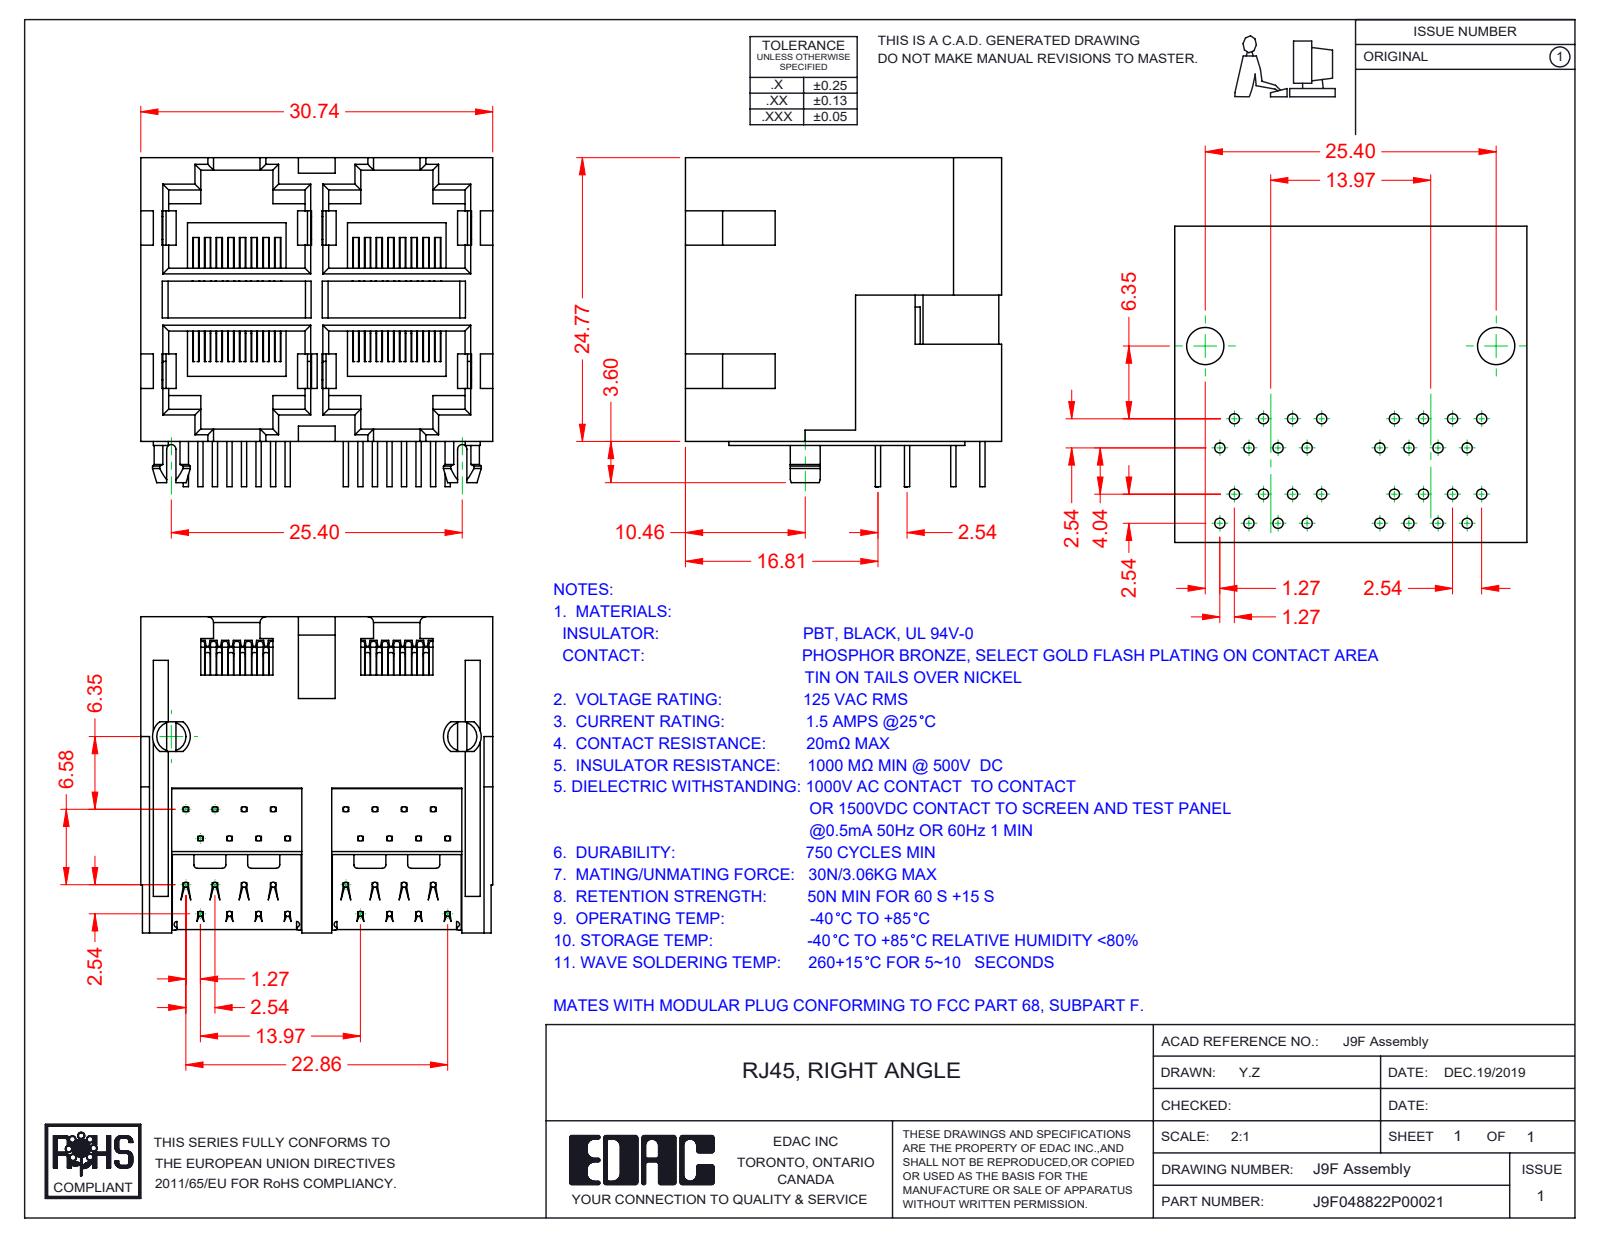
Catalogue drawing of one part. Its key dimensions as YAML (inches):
part_name: "9F Insulator; 9F Contacts Upper; 9F Contacts Lower; RJ9F048822P00021 (+2 more)"
step_written_by: "SolidWorks 2016 (CONFIG_CONTROL_DESIGN)"
units: inches
bodies: {solids: 37, faces: 2810, planar: 1899, cylindrical: 557, other: 354}
overall_size: [1.21, 1.13, 1.087]
volume: 0.718
surface_area: 30.65
round_bosses_or_shafts:
  - {diameter: 0.018, count: 144}
partial_cylinders:
  - {radius: 0.008, count: 63}
  - {radius: 0.02, count: 25}
  - {radius: 0.012, count: 9}
  - {radius: 0.01, count: 4}
  - {radius: 0.016, count: 2}
  - {radius: 0.018, count: 2}
  - {radius: 0.059, count: 2}
  - {radius: 0.065, count: 2}
face_to_face_distances: [0.55, 0.039, 0.014, 0.5, 0.591, 0.514, 0.472, 0.041, 0.536, 0.217]
